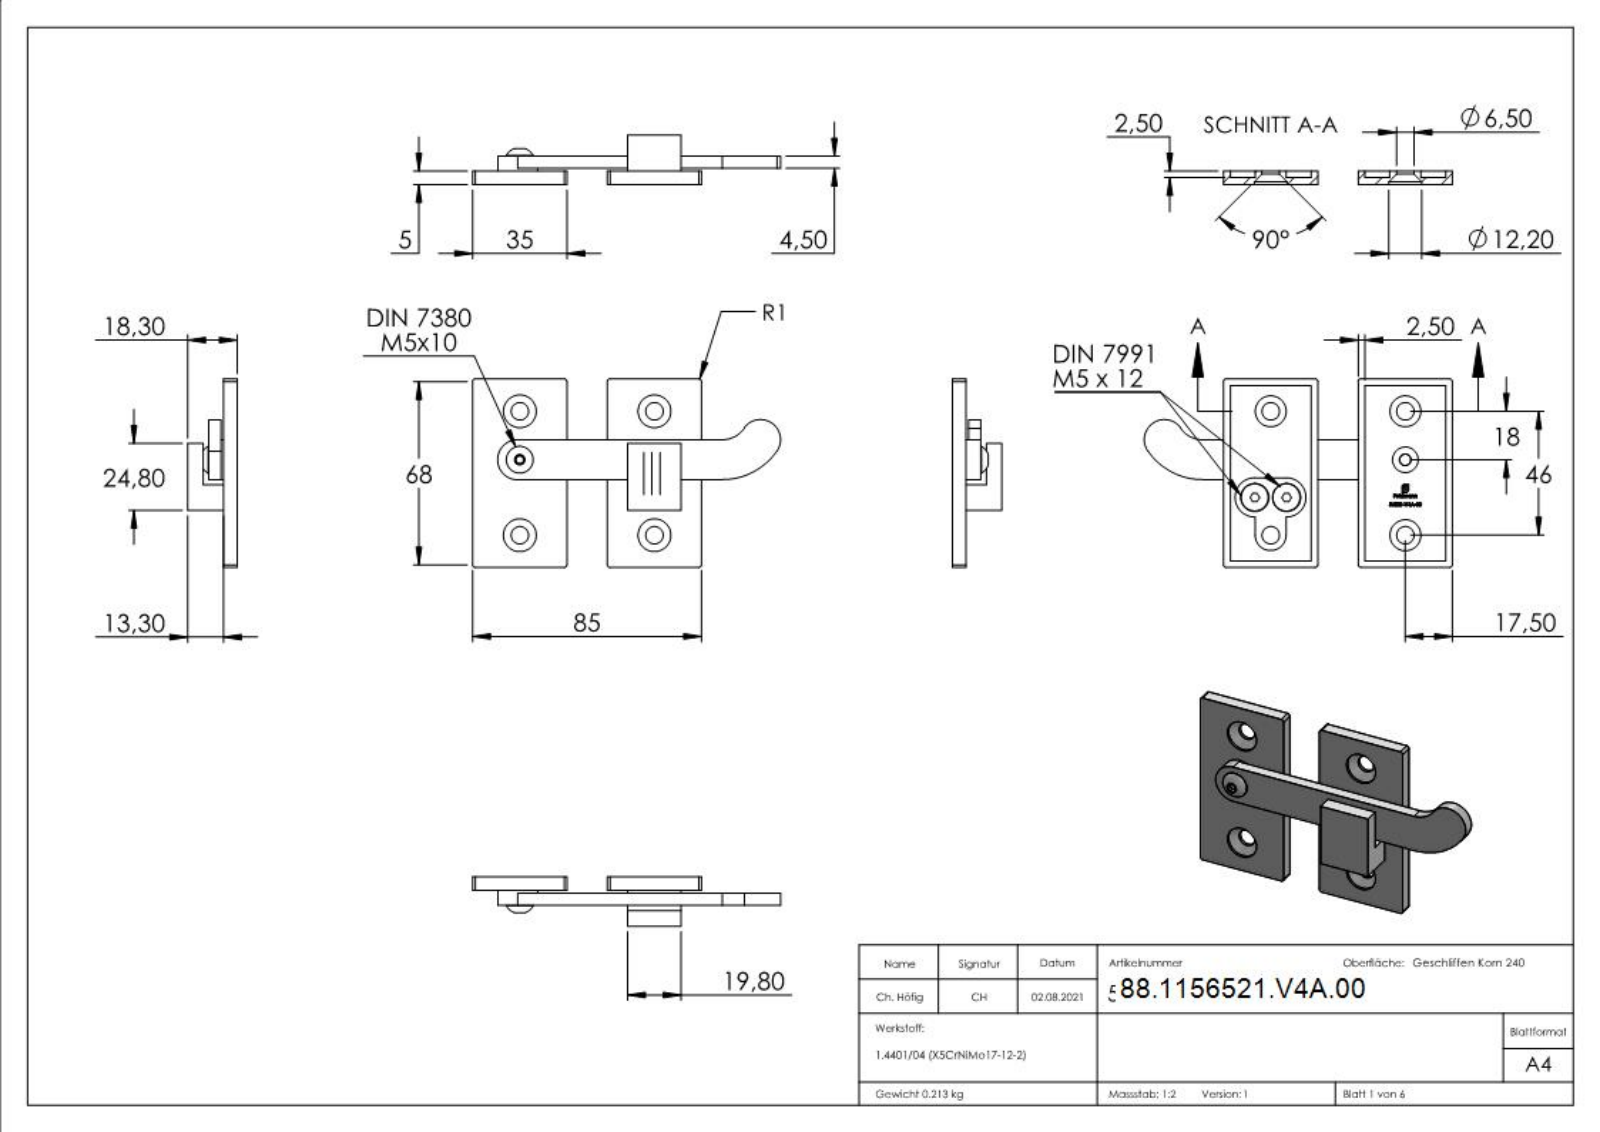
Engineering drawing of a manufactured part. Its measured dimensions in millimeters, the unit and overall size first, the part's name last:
Units: millimetres
Overall size (bounding box): 114.34 × 70 × 19.8
Round holes (diameter × count): ⌀6.5 ×4, ⌀12.2 ×4, ⌀4.2 ×3, ⌀5.5 ×3, ⌀10.5 ×2
Round bosses / shafts (diameter × count): ⌀11.5 ×3, ⌀10 ×3, ⌀5 ×3, ⌀14.8 ×1, ⌀9.5 ×1
Partial cylindrical surfaces — rounded edges, fillets, slot ends (radius × count): R1 ×8, R7.25 ×2, R5.75 ×1, R7.4 ×1, R10.02 ×1, R24.8 ×1
Main face-to-face distances: 2.5, 5.5, 8, 5, 10.5, 4.5, 6, 3.5, 1, 50
Hole centre spacings: 15.19, 32.54, 46, 46.27, 50, 57.63, 67.94, 11.8
Volume: 26 673 mm³ · Surface area: 21 155 mm²
Bodies: 7 solids, 425 faces (240 planar, 41 cylindrical, 144 other)
Part name (STEP PRODUCT): 5652X-V4A-XX Teil1_56521-V4A-00 Teil2; DIN 7991 Konfig; 5652X-V4A-XX Teil1_56521-V4A-00 Teil1; 56521-V4A-00 (+6 more)
STEP written by: SolidWorks 2018 (CONFIG_CONTROL_DESIGN)
